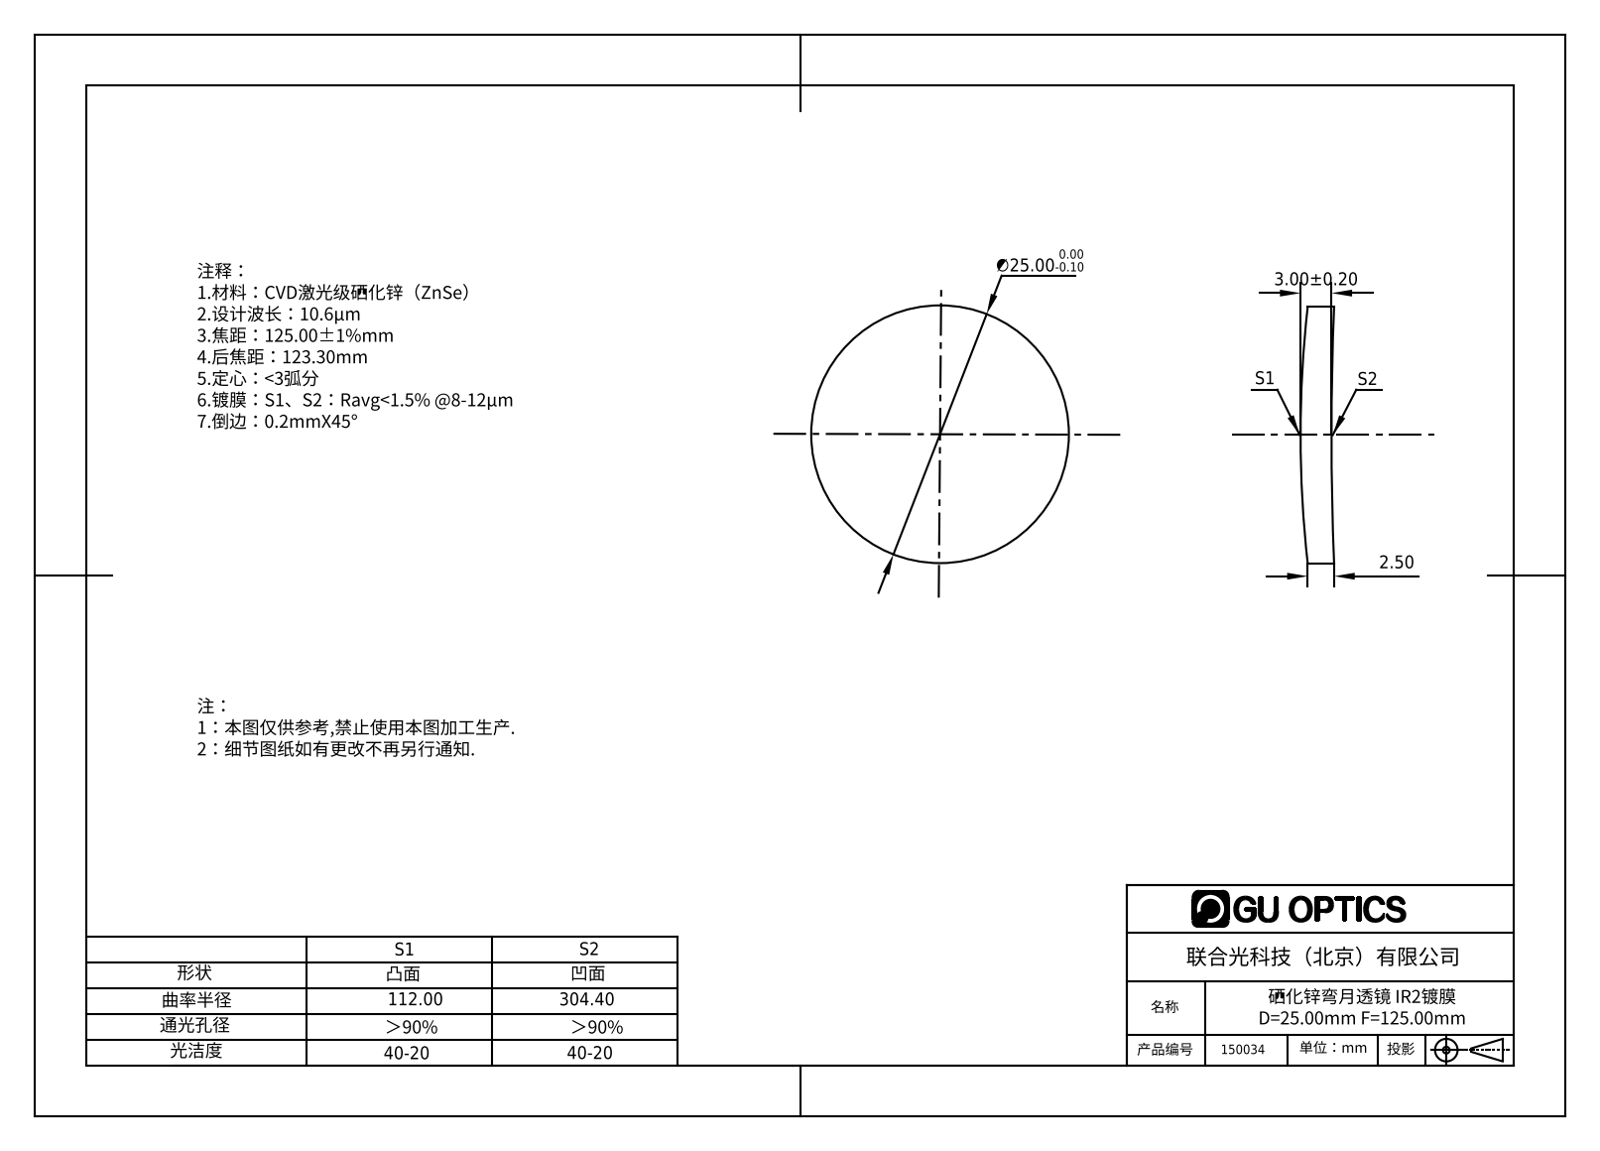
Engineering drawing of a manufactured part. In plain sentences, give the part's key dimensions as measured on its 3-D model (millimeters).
The part is named "150009". Its 3-D file was written by "SolidWorks 2016 (AUTOMOTIVE_DESIGN)". It is 1 solid with 6 faces: 0 planar, 2 cylindrical and 4 other. Overall it measures 25 by 25 by 3.26 millimeters. Its volume is 1 364 cubic millimeters and its surface area 1 184 square millimeters. Round bosses or shafts: 1 of diameter 25.
